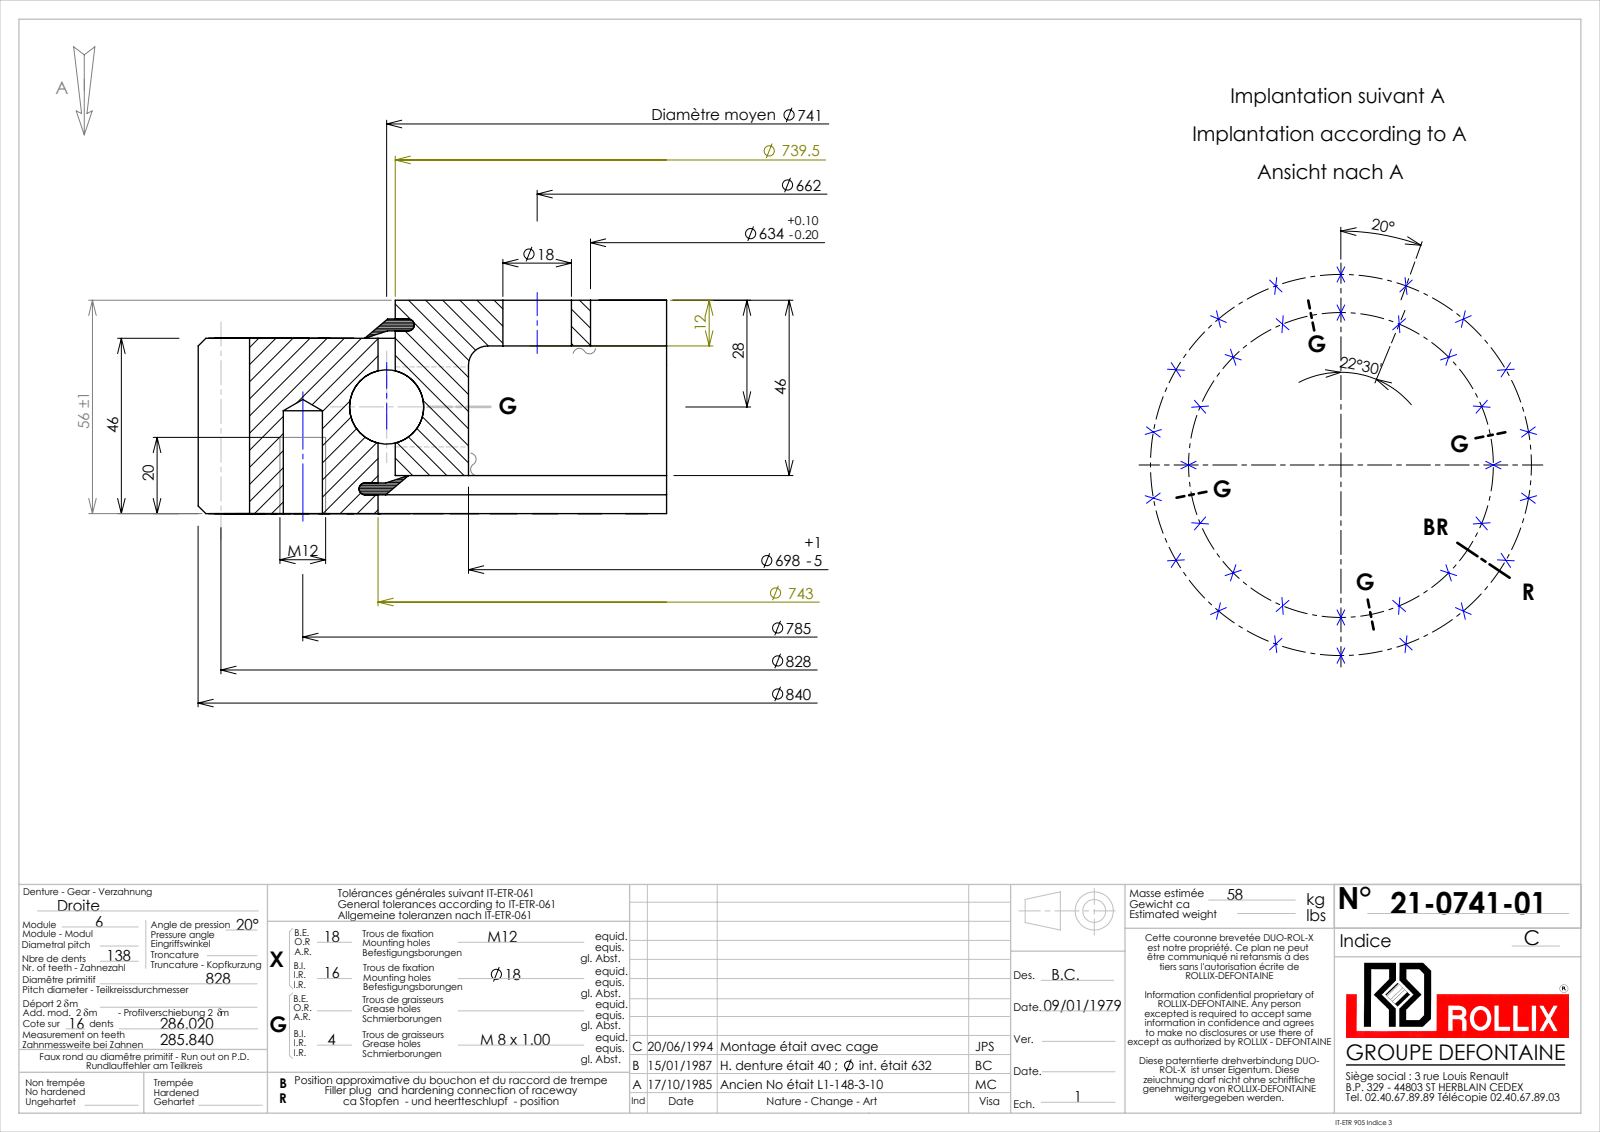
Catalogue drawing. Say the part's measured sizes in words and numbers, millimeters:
The part is named "21-0741-01". Its 3-D file was written by "SolidWorks 2016 (CONFIG_CONTROL_DESIGN)". It is 9 solids with 1088 faces: 329 planar, 377 cylindrical and 382 other. Overall it measures 840 by 839.89 by 56 millimeters. Its volume is 6 953 000 cubic millimeters and its surface area 1 204 000 square millimeters. Round holes: 18 of diameter 10.25, 16 of diameter 18, 4 of diameter 7, 1 of diameter 634, 1 of diameter 698, 1 of diameter 745.5. Round bosses or shafts: 4 of diameter 8, 1 of diameter 736.5. Partial cylindrical surfaces (rounded edges, fillets, slot ends): 1 of radius 406.5, 1 of radius 420. The main face-to-face distances are 10, 46, 56, 44, 2, 12, 34, 36, 4.95, 51.05. The hole center spacings are 392.5, 136.31, 679.83, 773.07, 268.48, 601.34, 504.59, 331.
